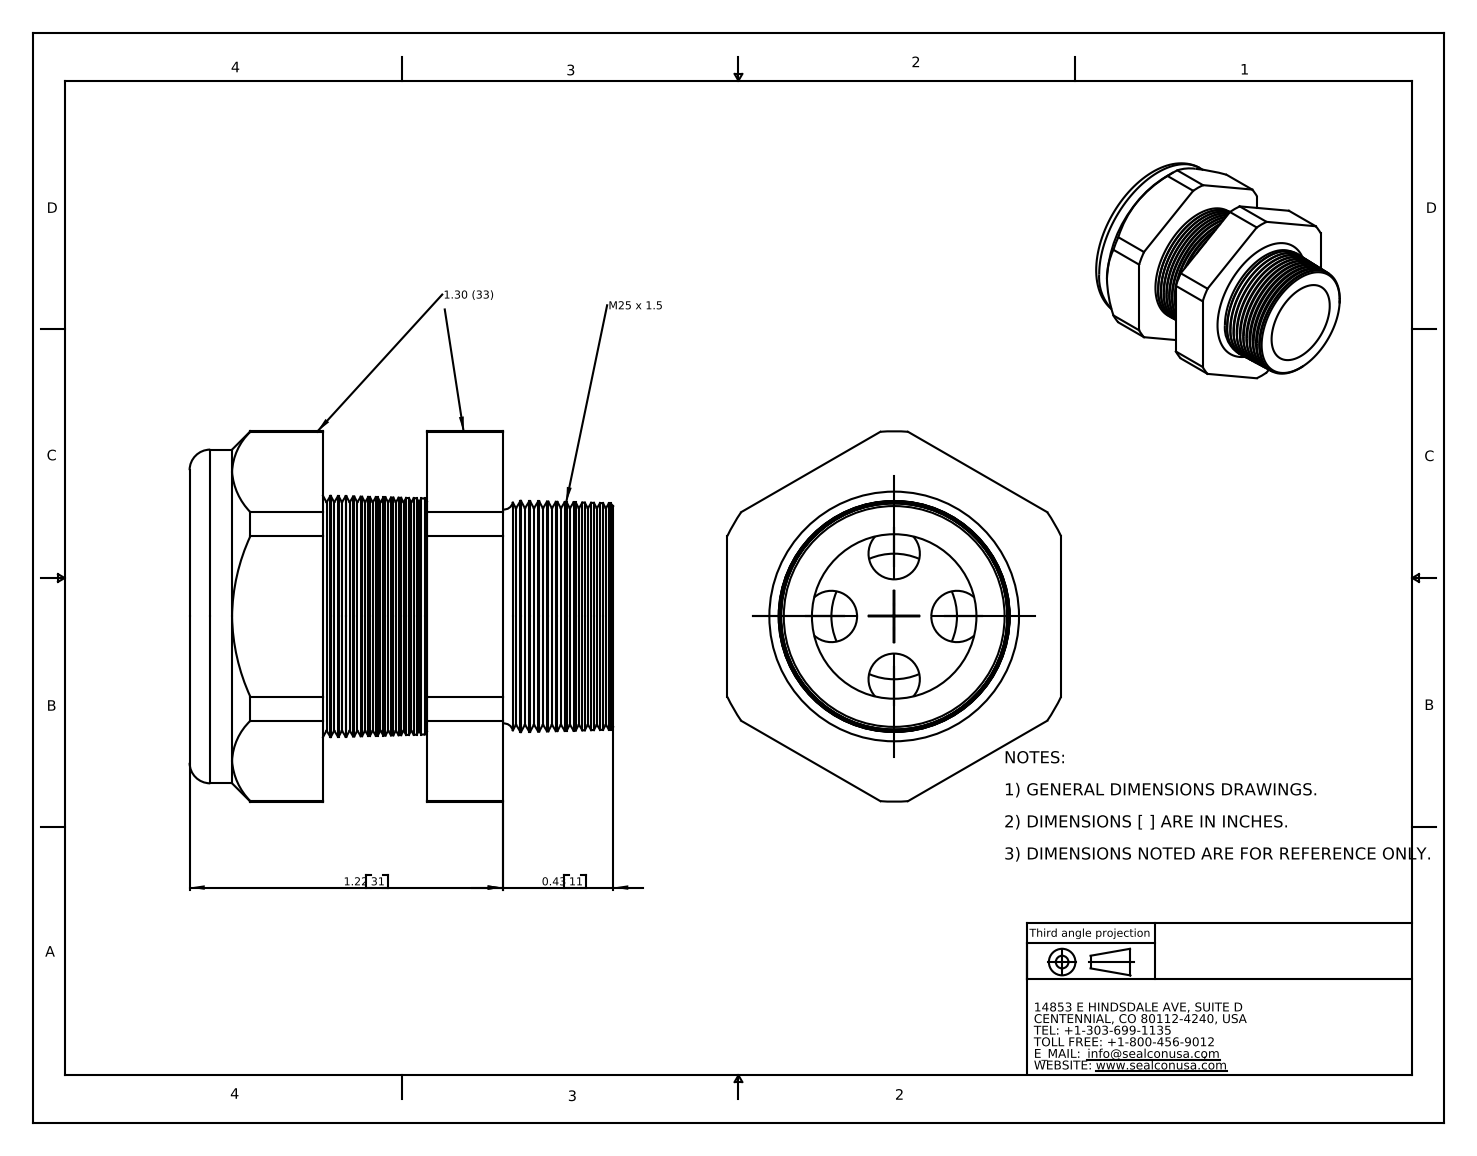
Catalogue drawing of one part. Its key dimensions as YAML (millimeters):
part_name: "CD25M6-GY"
step_written_by: "SolidWorks 2007 (CONFIG_CONTROL_DESIGN)"
units: millimeters
bodies: {solids: 2, faces: 214, planar: 20, cylindrical: 28, other: 166}
overall_size: [41.9, 36.7, 33]
volume: 18850
surface_area: 11050
round_holes:
  - {diameter: 5.1, count: 4}
  - {diameter: 17.5, count: 1}
  - {diameter: 18, count: 1}
round_bosses_or_shafts:
  - {diameter: 33, count: 1}
partial_cylinders:
  - {radius: 18.3, count: 1}
face_to_face_distances: [33, 10.3, 17.8, 7.5, 13.2, 23.5, 31, 8.9, 4.3, 14.6]
hole_center_spacings: [6.2, 8.8, 12.4]
